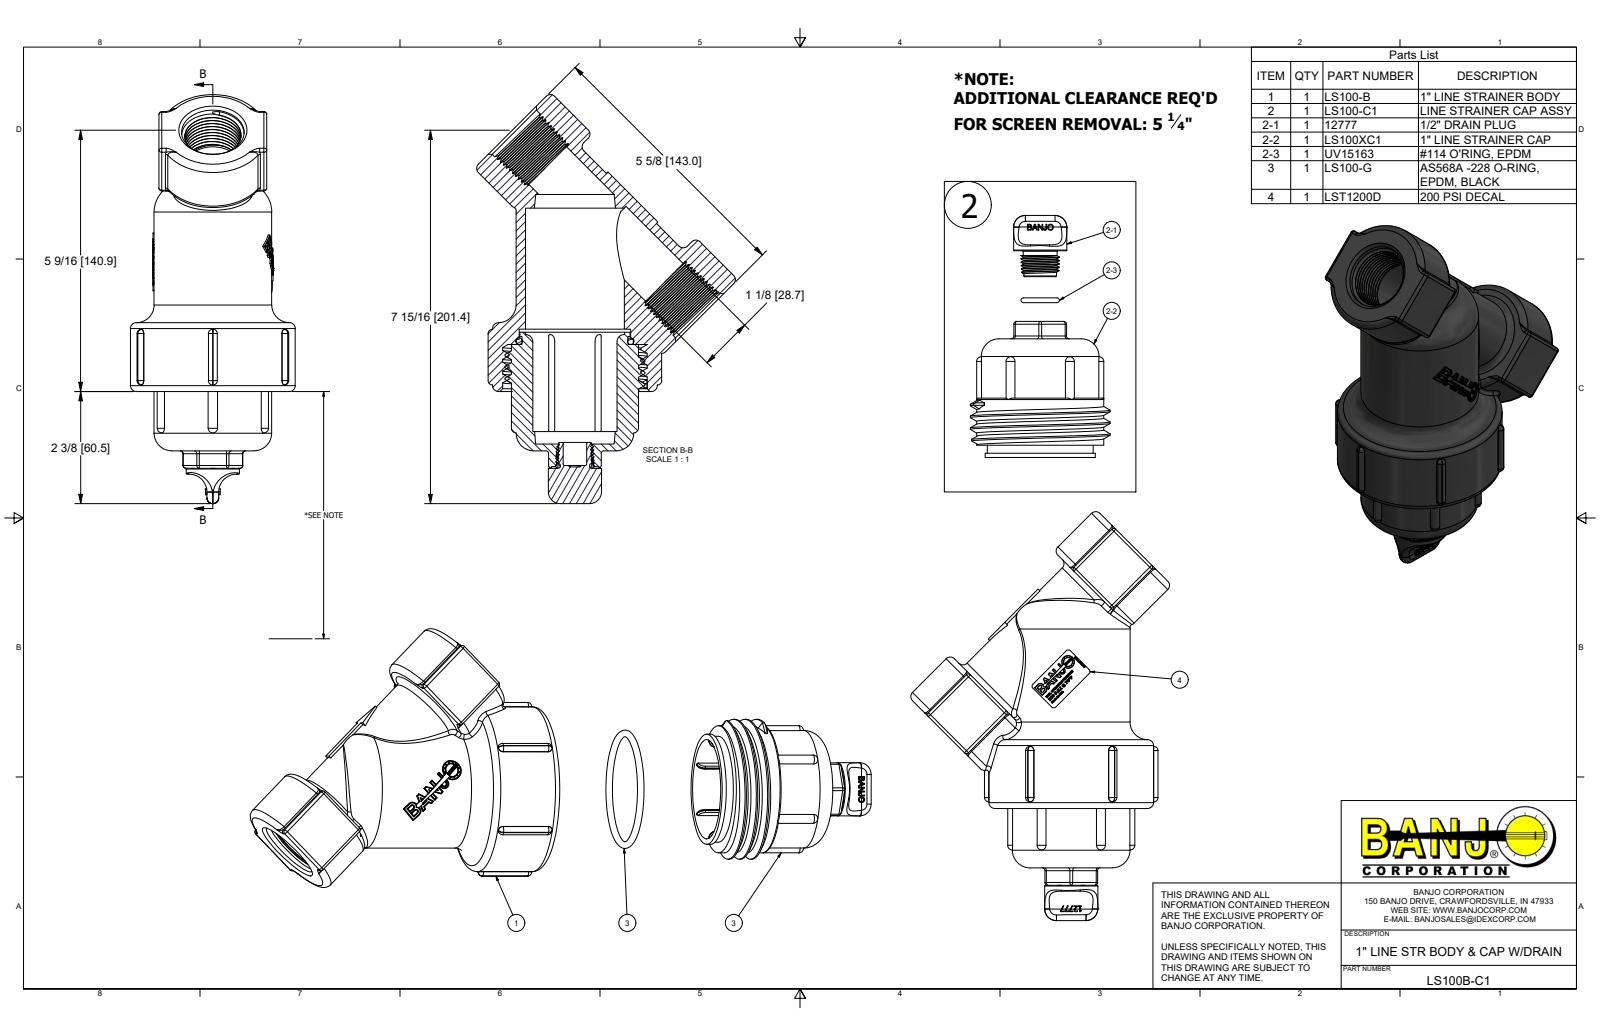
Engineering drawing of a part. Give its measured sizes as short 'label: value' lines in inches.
name: LS100B-C1; LS100-B; LS100-C1; LS100XC1 (+5 more)
written by: Autodesk Inventor 2019 (AUTOMOTIVE_DESIGN)
unit: in
bodies: 7 solids, 2066 faces (1092 planar, 302 cylindrical, 672 other)
size: 26.366 × 26.366 × 3.5
volume: 24.37 in³; area: 458.1 in²
holes: 2× ⌀1.13, 1× ⌀0.181, 1× ⌀0.257, 1× ⌀0.272, 1× ⌀0.385, 1× ⌀0.5, 1× ⌀1.005, 1× ⌀2.1, 1× ⌀2.11, 1× ⌀2.371, 1× ⌀2.48, 1× ⌀2.799
bosses: 1× ⌀3.5, 1× ⌀2.971, 1× ⌀2.7, 1× ⌀2.5, 1× ⌀2.34, 1× ⌀2.25, 1× ⌀1.13, 1× ⌀0.5
rounds: 54× R0.06, 35× R0.09, 18× R0.03, 7× R0.1, 6× R0.15, 2× R0.026, 2× R0.033, 2× R0.039
face distances: 2.29, 5.629, 2.115, 1.26, 0.07, 2.895, 5.01, 2.57, 0.145, 2.26
hole spacings: 0.919
